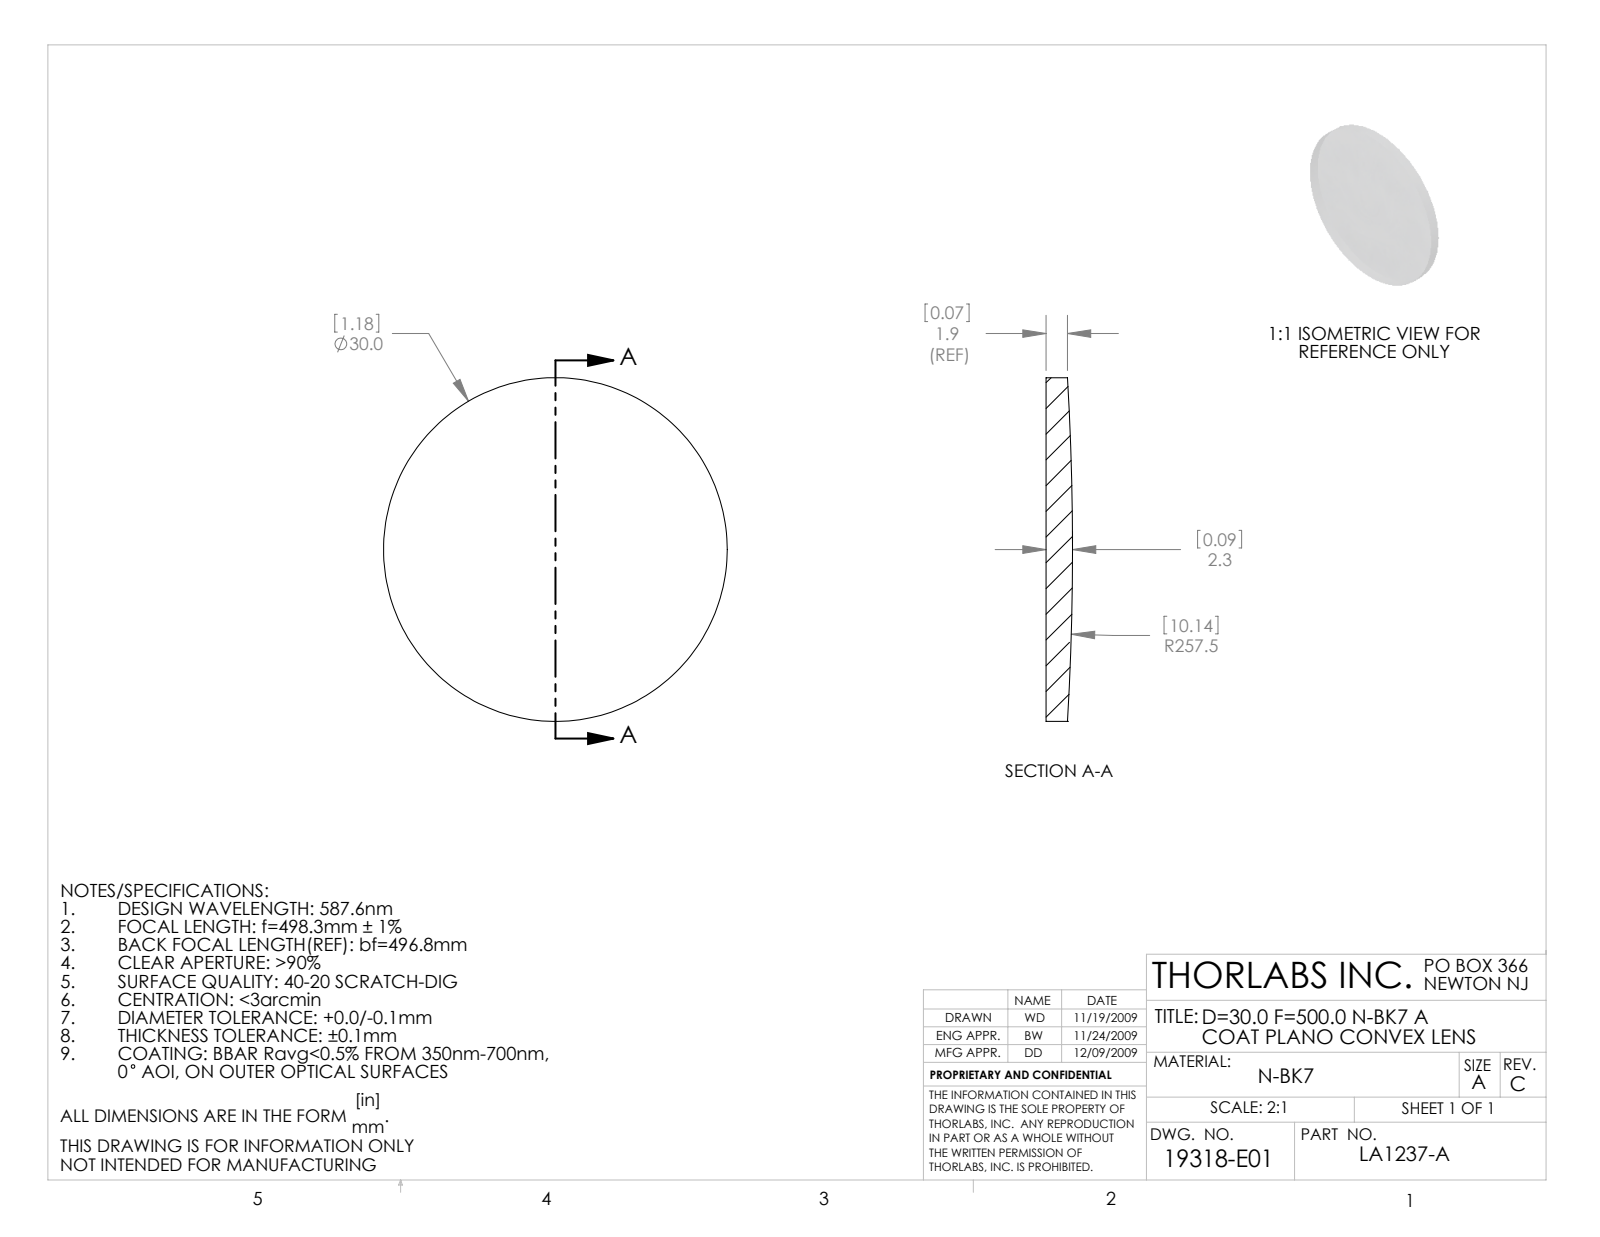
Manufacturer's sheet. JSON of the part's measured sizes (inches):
{"part_name": "19318-E0W", "step_written_by": "SolidWorks 2009 (AUTOMOTIVE_DESIGN)", "units": "inches", "bodies": {"solids": 1, "faces": 5, "planar": 1, "cylindrical": 2, "other": 2}, "overall_size": [1.181, 1.181, 0.091], "volume_in3": 0.09, "surface_area_in2": 2.466, "round_bosses_or_shafts": [[1.181, 1]]}
